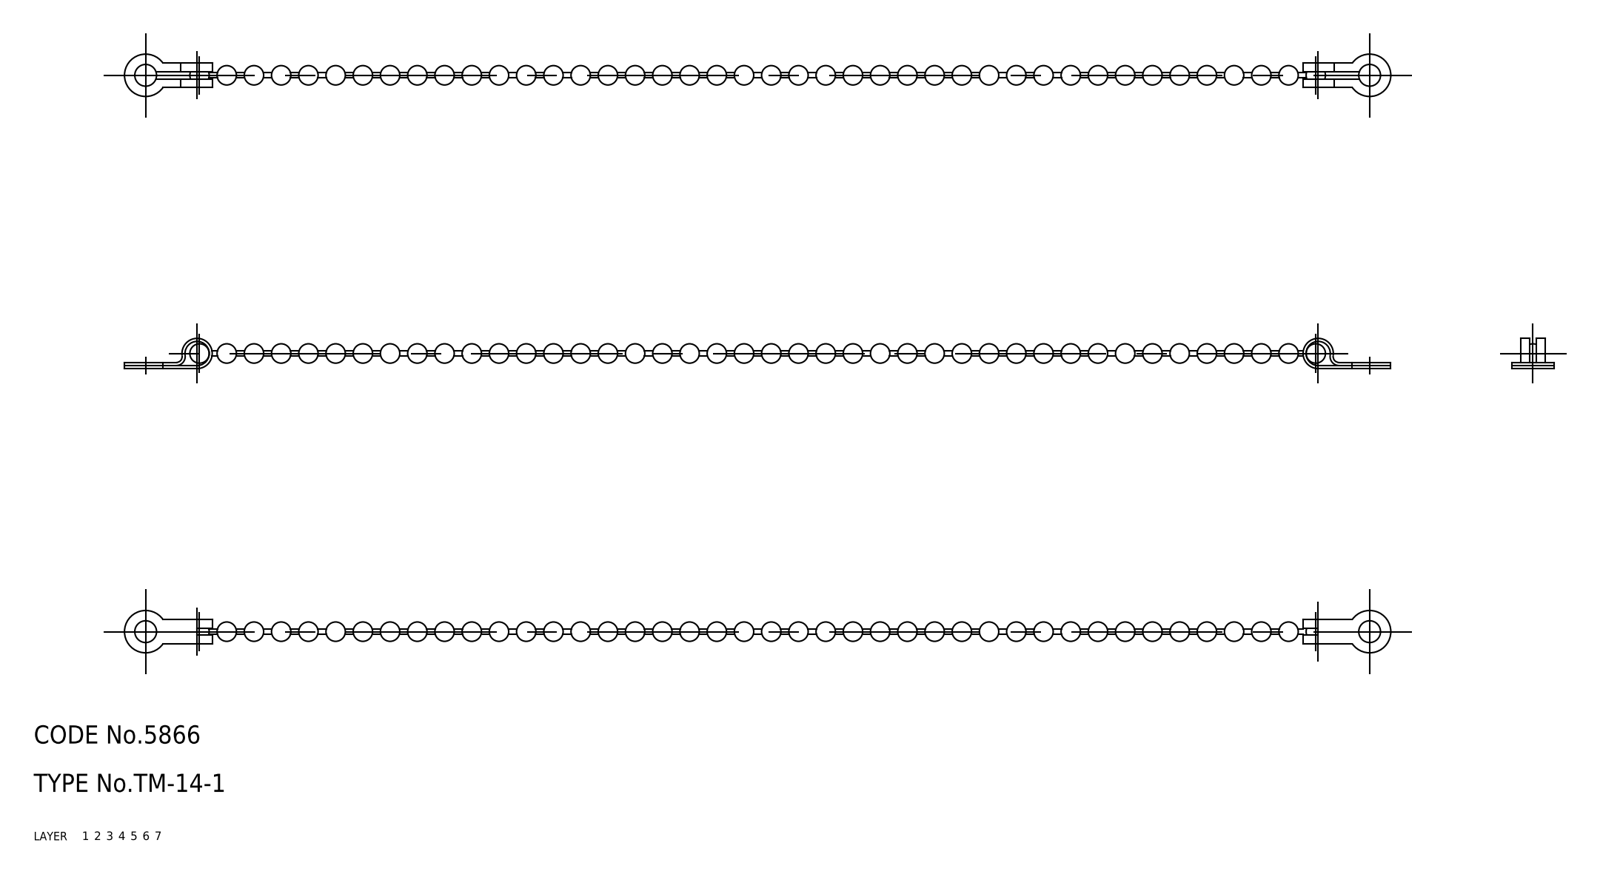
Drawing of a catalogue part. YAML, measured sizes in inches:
part_name: "terminal; chain; joint; TM_14_1_10551_36"
step_written_by: "CADfix (AUTOMOTIVE_DESIGN)"
units: inches
bodies: {solids: 45, faces: 174, planar: 0, cylindrical: 0, other: 174}
overall_size: [8.24, 0.276, 0.197]
volume: 0.05
surface_area: 4.258
